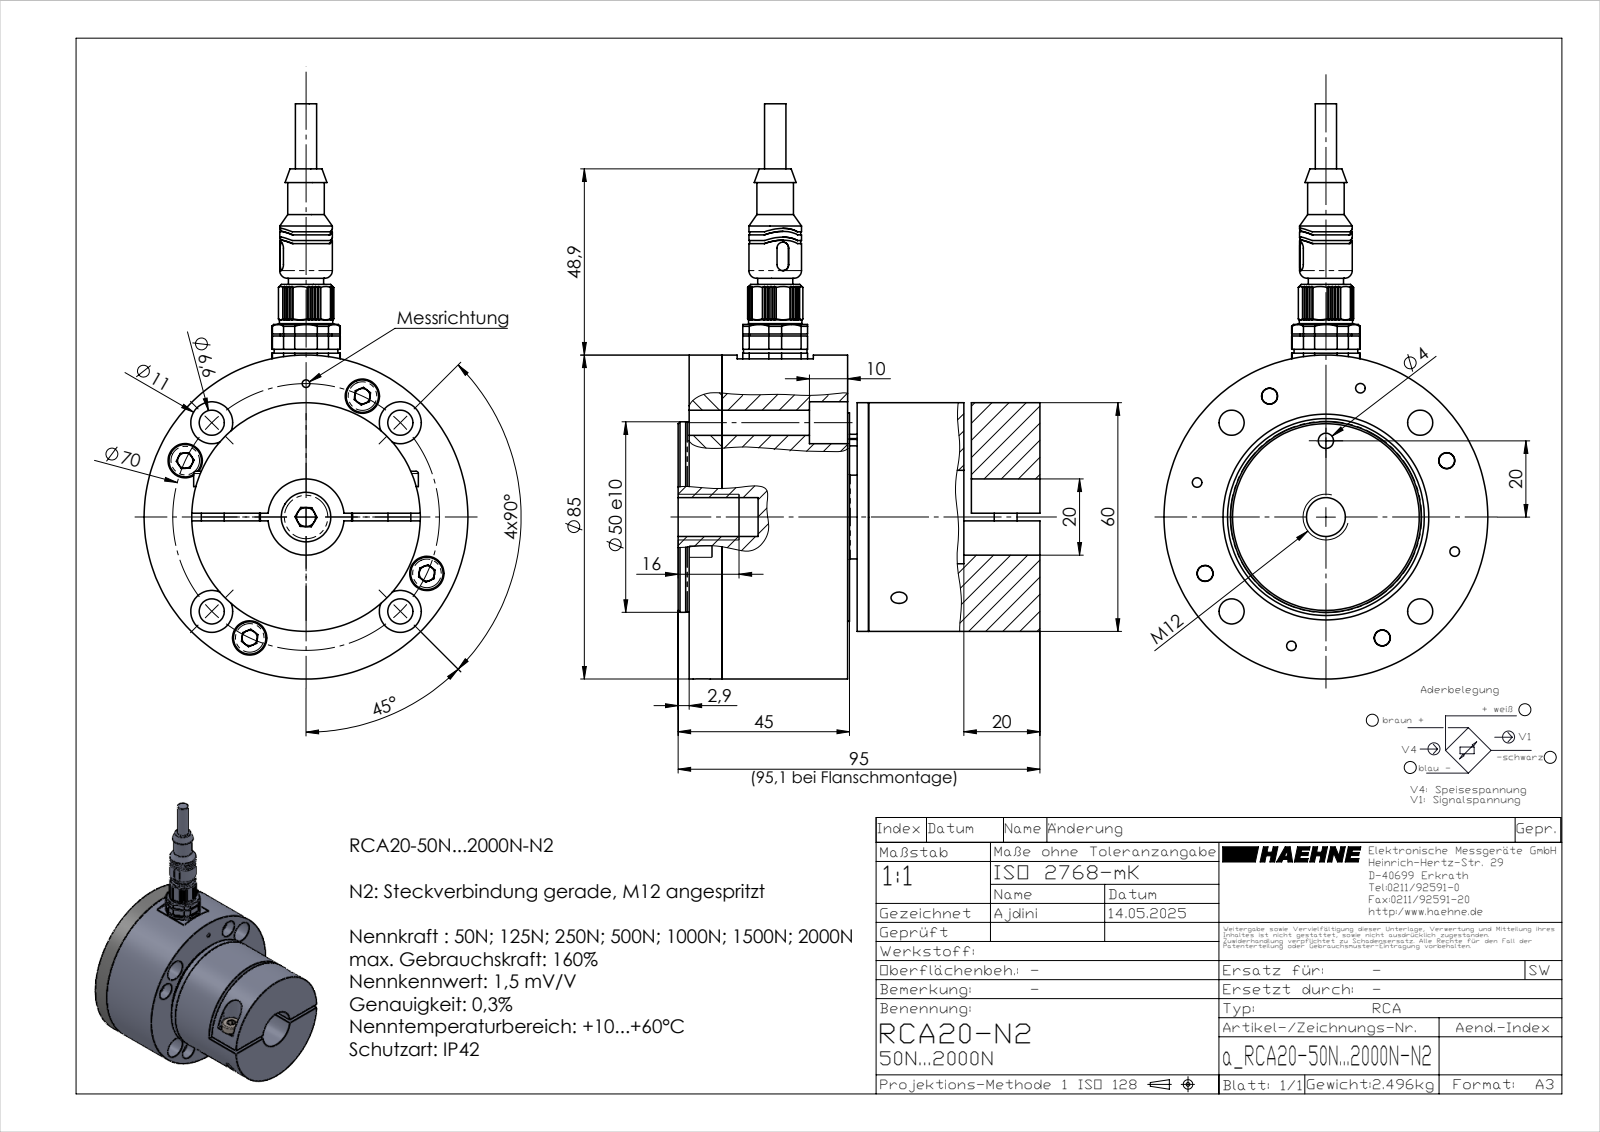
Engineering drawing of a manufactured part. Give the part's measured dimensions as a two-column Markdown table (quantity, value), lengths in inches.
| quantity | value |
| --- | --- |
| part name | inafag_1203-tvh_7zkvytp7yxkimpdvw8sj0b5w4_02; a_RCA20-50N...2000N-N2; inafag_1203-tvh_7zkvytp7yxkimpdvw8sj0b5w4_25; inafag_1203-tvh_7zkvytp7yxkimpdvw8sj0b5w4_20 (+8 more) |
| STEP written by | SolidWorks 2023 (AUTOMOTIVE_DESIGN) |
| units | inches |
| bodies | 53 solids, 1170 faces (648 planar, 300 cylindrical, 222 other) |
| overall size | 5.942 × 3.744 × 3.346 |
| volume | 22.48 in³ |
| surface area | 174.8 in² |
| round holes (diameter × count) | 0.134 × 9, 0.098 × 8, 0.26 × 6, 0.165 × 5, 0.433 × 5, 0.043 × 4, 0.045 × 4, 0.063 × 4, 0.073 × 4, 0.157 × 4, 0.209 × 4, 0.354 × 4 |
| round bosses / shafts (diameter × count) | 0.118 × 9, 0.224 × 8, 0.335 × 4, 0.197 × 4, 0.071 × 4, 0.061 × 4, 0.059 × 4, 0.039 × 4 |
| partial cylindrical surfaces (radius × count) | 0.008 × 16, 0.012 × 9, 0.016 × 4, 0.021 × 4, 0.039 × 4, 0.05 × 4, 0.472 × 4, 0.063 × 2 |
| main face-to-face distances | 0.118, 0.079, 0.339, 1.854, 1.772, 0.457, 1.181, 1.969, 1.398, 1.972 |
| hole center spacings | 1.378, 1.949, 0.976, 0.992, 1.291, 2.013, 2.223, 0.098 |
